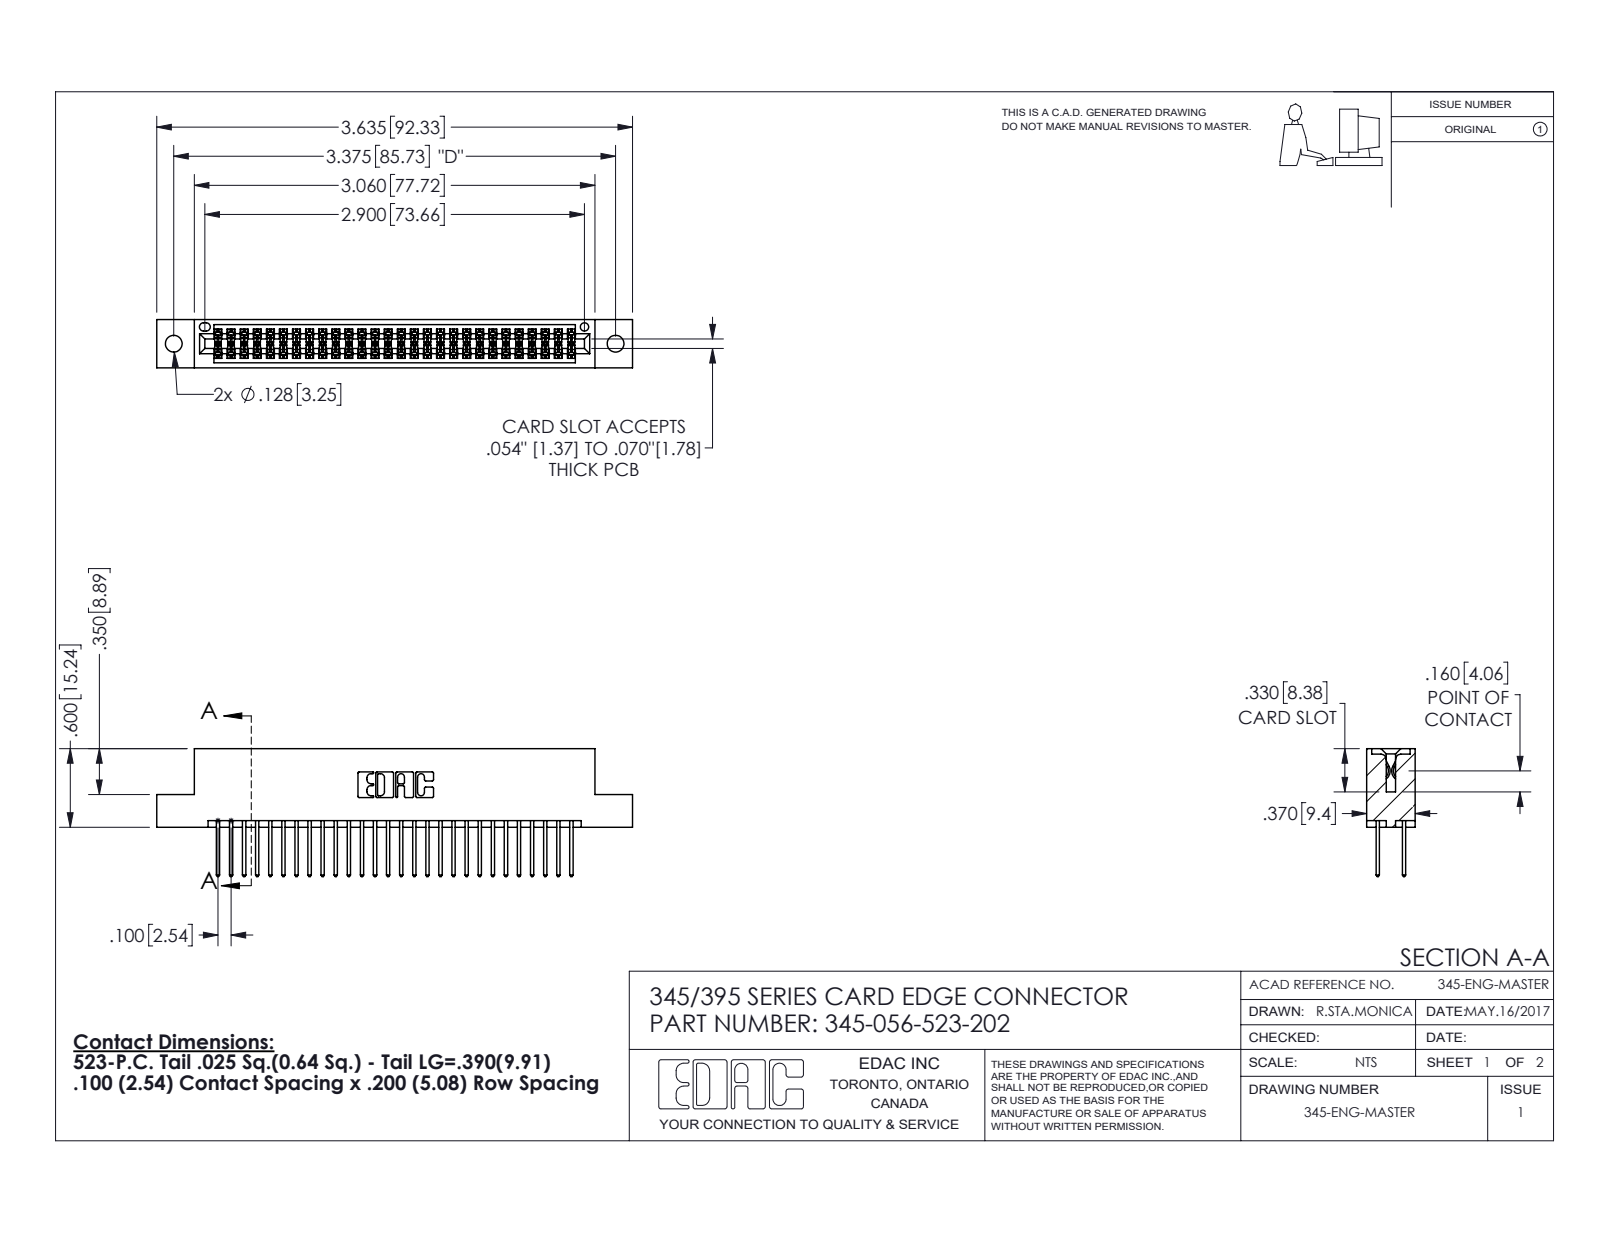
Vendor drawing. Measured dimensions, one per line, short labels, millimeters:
name: 345-292-001_345-293-123; 345-056-523-202; 345 Part_Flush Mounting Lugs - 0.128 Dia
written by: SolidWorks 2016 (CONFIG_CONTROL_DESIGN)
unit: mm
bodies: 57 solids, 2926 faces (1928 planar, 998 cylindrical, 0 other)
size: 92.3 × 24.8 × 9.4
volume: 8 910 mm³; area: 13 150 mm²
holes: 2× ⌀3.3, 1× ⌀1.6
rounds: 84× R0.2, 56× R0.3, 22× R0.3, 6× R0.2, 6× R0.8, 3× R0.7, 2× R0.4, 2× R0.5
face distances: 7.6, 1.8, 5.1, 2.5, 6.9, 0.6, 9.4, 5.7, 4.4, 3.8
hole spacings: 6.9, 79.8, 85.7
